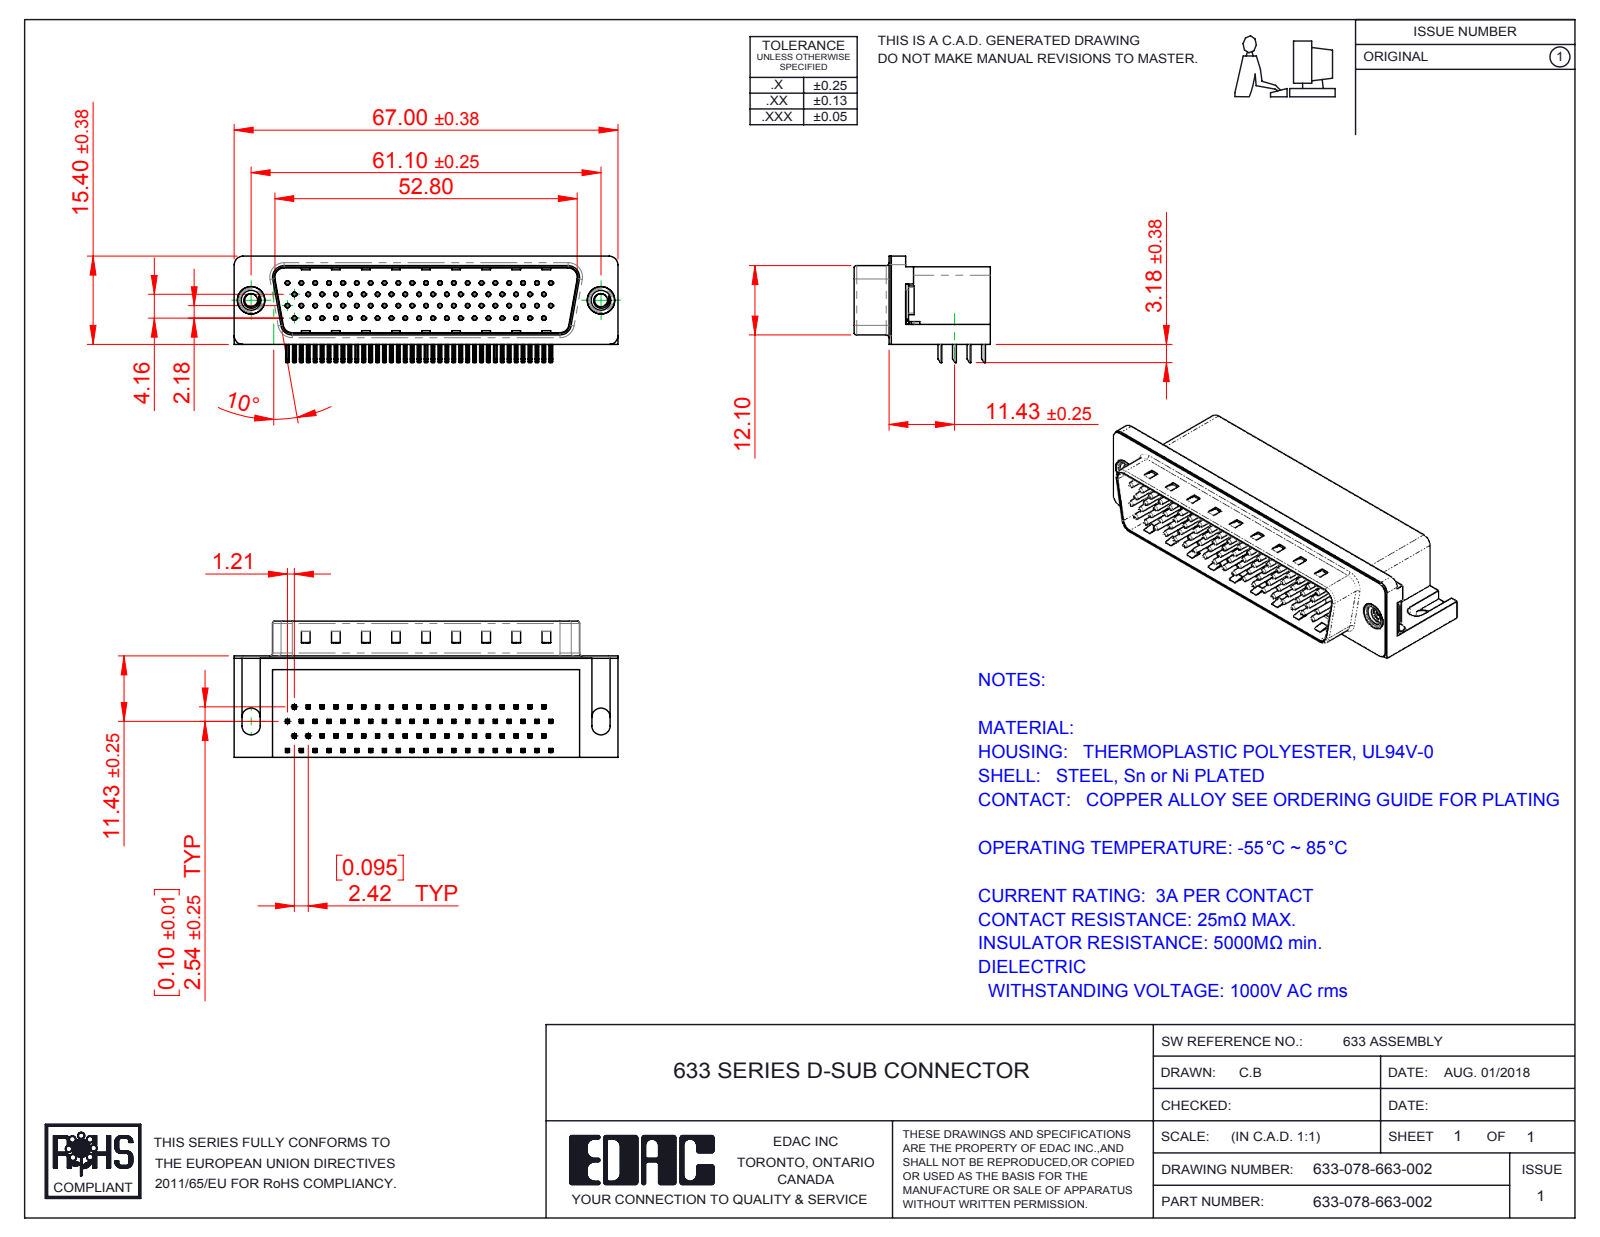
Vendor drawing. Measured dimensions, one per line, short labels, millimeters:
name: 633-078-663-002; 633 4-40 Threaded Rivet; 633 Housing_78 Contact; 633 Contact Top_78 Contact (+5 more)
written by: SolidWorks 2016 (CONFIG_CONTROL_DESIGN)
unit: mm
bodies: 84 solids, 6270 faces (3979 planar, 1774 cylindrical, 517 other)
size: 67 × 23.8 × 18.58
volume: 14 566 mm³; area: 16 125 mm²
holes: 78× ⌀0.35, 78× ⌀0.8, 2× ⌀2.26, 2× ⌀4, 2× ⌀4.8, 2× ⌀5
bosses: 78× ⌀0.75, 2× ⌀4.9, 2× ⌀4.75, 2× ⌀3.9
rounds: 320× R0.25, 156× R0.12, 16× R1, 9× R0.5, 8× R1.6, 6× R1.5, 4× R0.45, 4× R0.9
face distances: 0.4, 13.2, 17.3, 11.7, 13.35, 2.05, 13.75, 1.65, 11.9, 1.85
hole spacings: 2.42, 4.84, 7.26, 9.68, 6.26, 7.13, 12.1, 8.62
